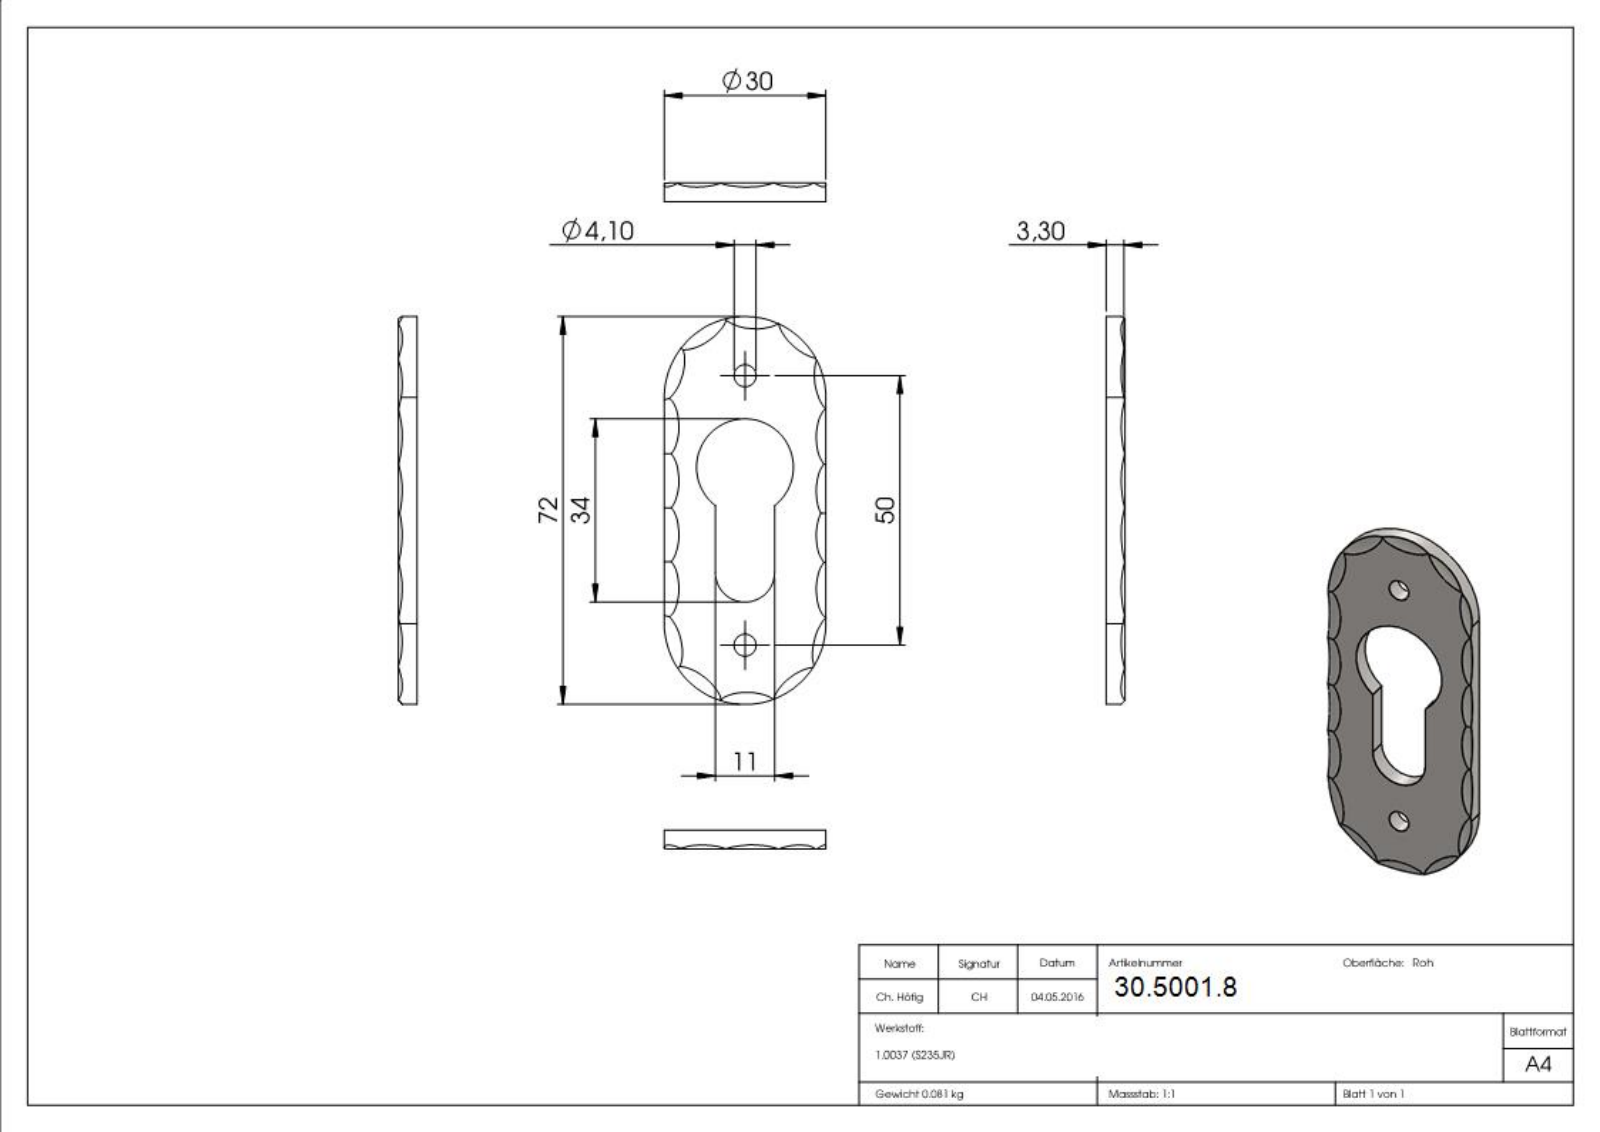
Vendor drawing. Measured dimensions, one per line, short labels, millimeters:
name: 8151
written by: SolidWorks 2015 (CONFIG_CONTROL_DESIGN)
unit: mm
bodies: 1 solid, 529 faces (114 planar, 145 cylindrical, 270 other)
size: 72 × 30.01 × 3.7
volume: 5 000 mm³; area: 3 968 mm²
holes: 2× ⌀4.1
rounds: 17× R10, 7× R11.56, 5× R1, 3× R11.56, 2× R15, 1× R5.5, 1× R9
face distances: 30, 3.5, 9.5, 20.5, 11, 3.4, 1.22, 6.44, 5.22, 1.78
hole spacings: 50
